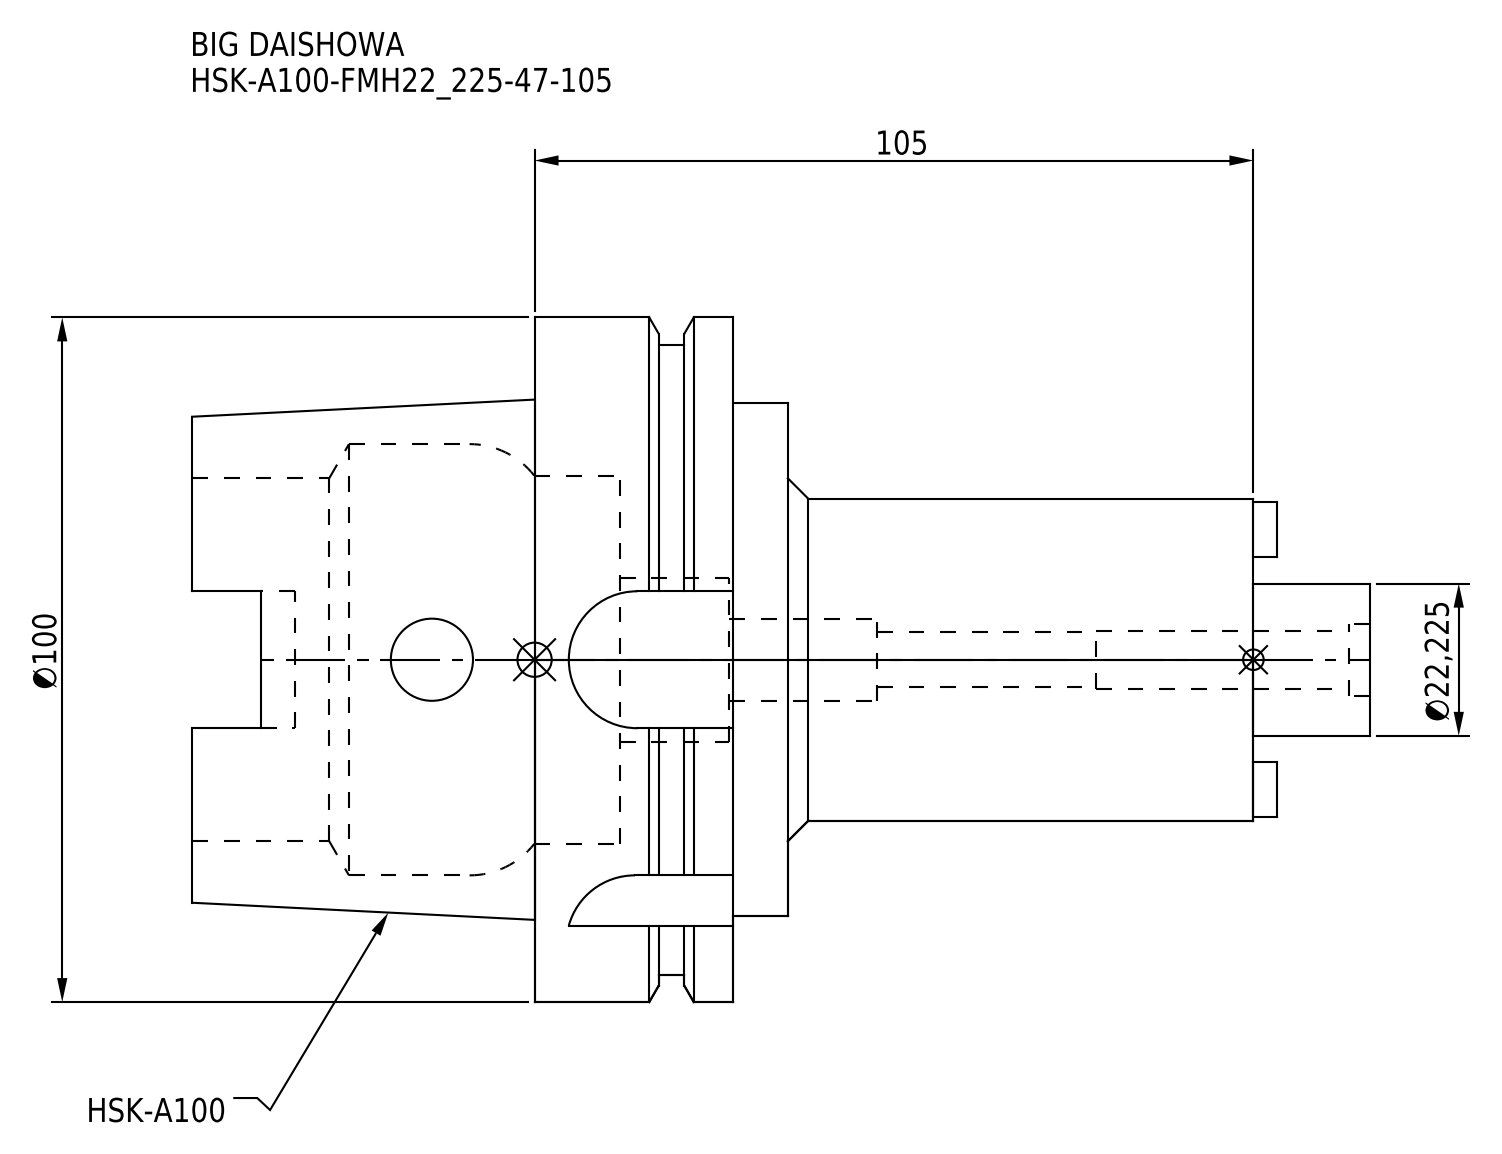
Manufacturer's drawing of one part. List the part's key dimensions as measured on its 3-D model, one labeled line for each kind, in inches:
Part name (STEP PRODUCT): HSK-A100-FMH22_225-47-105
STEP written by: CREO PARAMETRIC BY PTC INC, 2016380 (AUTOMOTIVE_DESIGN)
Units: inches
Bodies: 1 solid, 109 faces (47 planar, 46 cylindrical, 16 other)
Overall size (bounding box): 6.772 × 3.937 × 3.937
Volume: 24.91 in³ · Surface area: 101.8 in²
Round holes (diameter × count): ⌀0.472 ×2, ⌀0.315 ×1, ⌀0.335 ×1, ⌀0.413 ×1, ⌀0.945 ×1, ⌀2.087 ×1, ⌀2.118 ×1, ⌀2.48 ×1
Round bosses / shafts (diameter × count): ⌀3.937 ×1, ⌀3.622 ×1, ⌀2.953 ×1, ⌀1.85 ×1, ⌀0.875 ×1
Partial cylindrical surfaces — rounded edges, fillets, slot ends (radius × count): R0.192 ×4, R0.394 ×4
Main face-to-face distances: 1.142, 0.315, 1.457, 0.967, 0.652, 0.49, 2.677, 2.992, 3.644, 4.134
